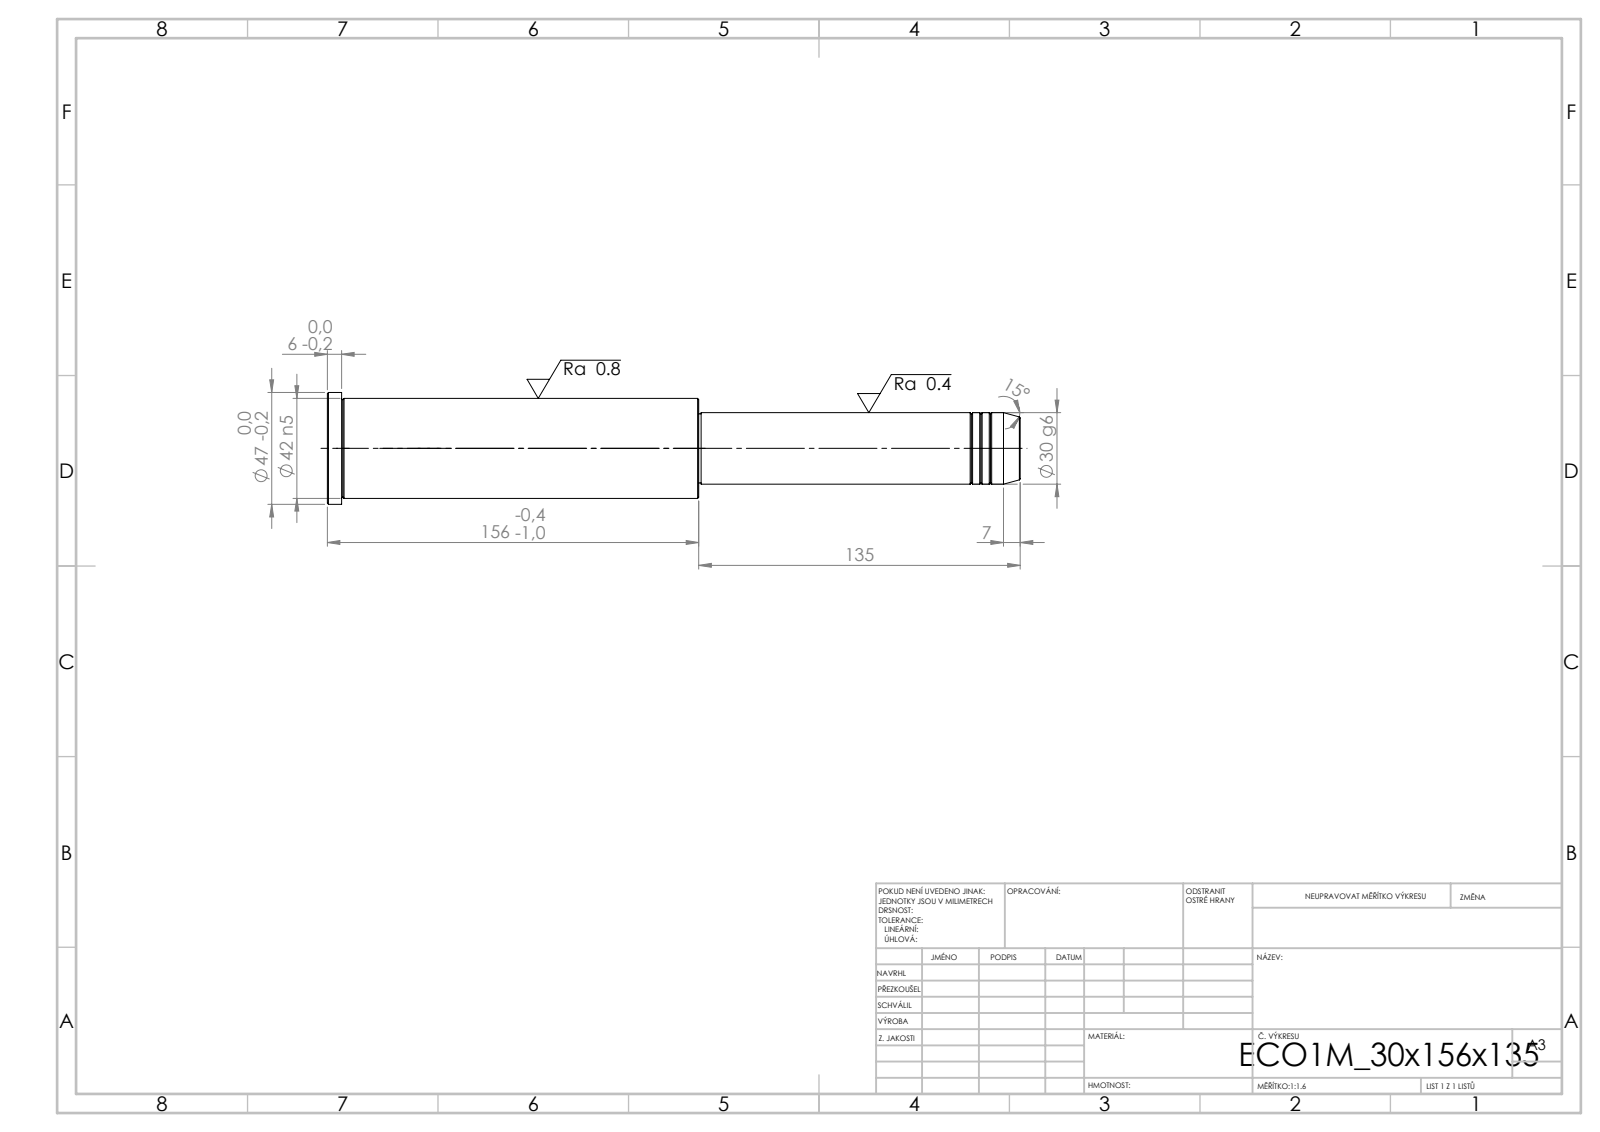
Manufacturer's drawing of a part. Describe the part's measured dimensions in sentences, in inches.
Its 3-D file was written by "SolidWorks 2019 (CONFIG_CONTROL_DESIGN)". It is 1 solid with 43 faces: 5 planar, 14 cylindrical and 24 other. Overall it measures 11.457 by 1.85 by 1.85 inches. Its volume is 19.09 cubic inches and its surface area 57.21 square inches. Round bosses or shafts: 1 of diameter 1.85, 1 of diameter 1.654, 1 of diameter 1.181, 1 of diameter 1.142. The main face-to-face distances are 6.142, 5.315, 11.457, 11.22, 5.906, 0.236, 5.276, 0.039, 5.945, 6.181.
